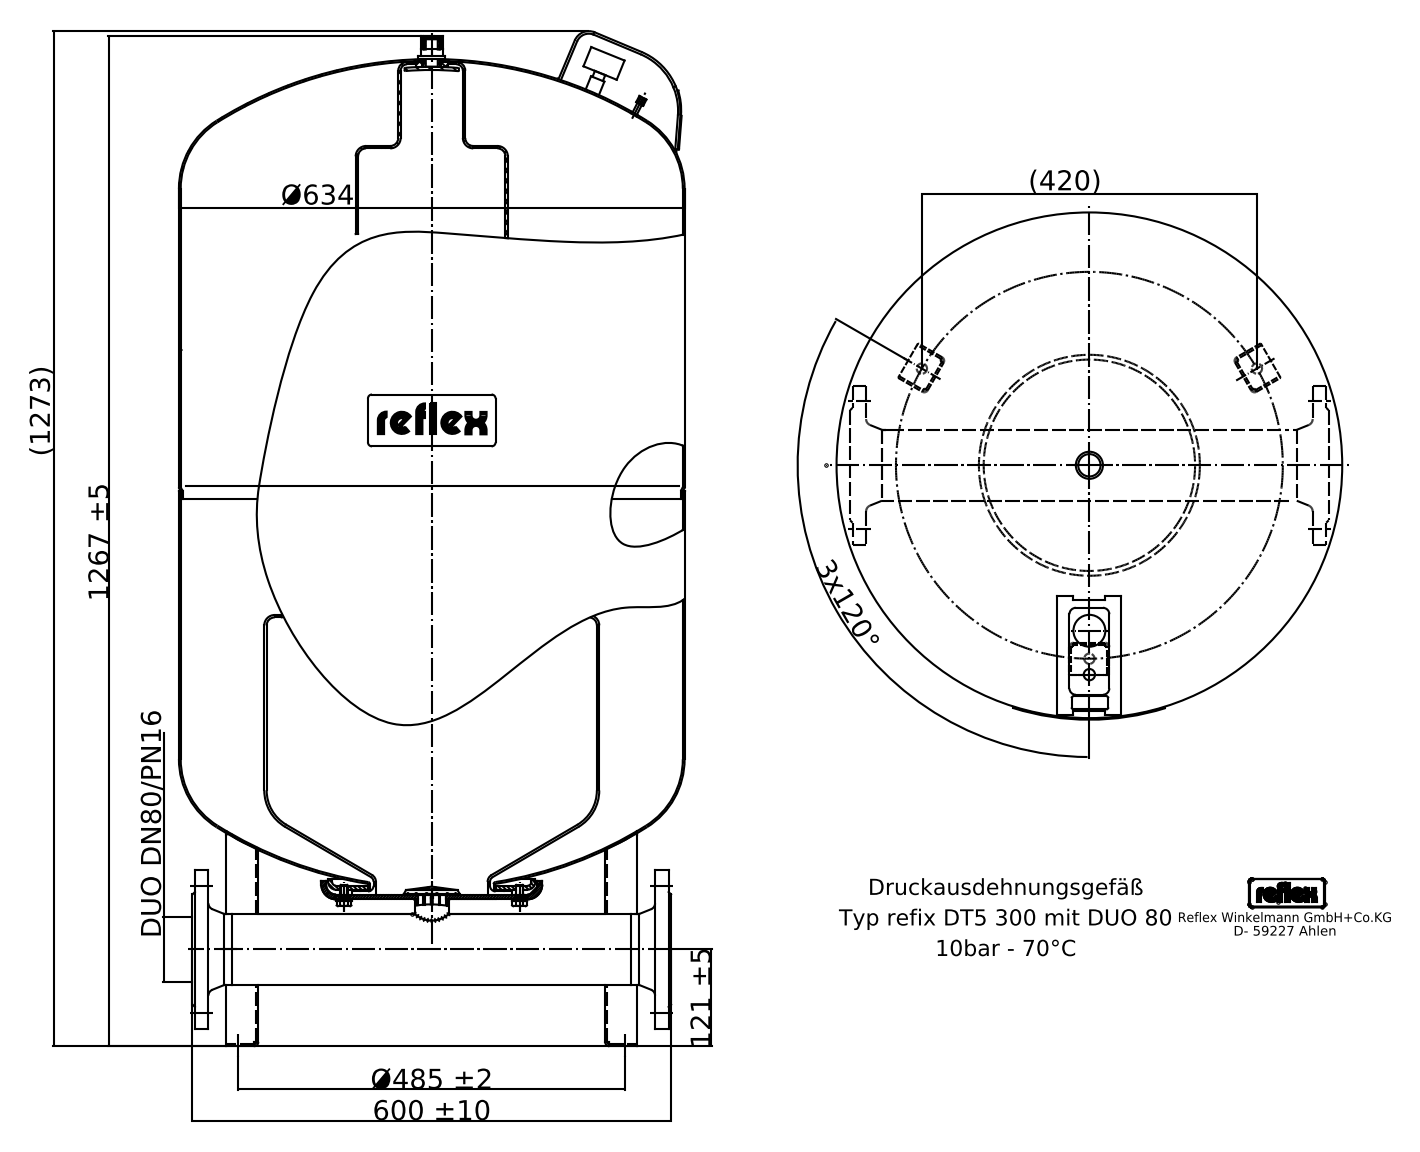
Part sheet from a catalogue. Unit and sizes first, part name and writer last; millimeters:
Units: millimetres
Overall size (bounding box): 1268.4 × 634 × 634
Round holes (diameter × count): ⌀19 ×8, ⌀13.4 ×3, ⌀2.48 ×1, ⌀3.8 ×1, ⌀4.3 ×1, ⌀4.4 ×1, ⌀5.45 ×1, ⌀7 ×1, ⌀8 ×1, ⌀11.4 ×1, ⌀88.9 ×1, ⌀157 ×1
Round bosses / shafts (diameter × count): ⌀10 ×9, ⌀634 ×1, ⌀260 ×1, ⌀230 ×1, ⌀200 ×1, ⌀62 ×1, ⌀42.4 ×1, ⌀34 ×1
Partial cylindrical surfaces — rounded edges, fillets, slot ends (radius × count): R1 ×15, R2.5 ×15, R5 ×15, R5.62 ×4, R2.25 ×3, R3.84 ×2, R6.75 ×2, R8 ×2
Main face-to-face distances: 716, 2.5, 47.5, 170, 886, 6, 176, 892, 50, 45
Hole centre spacings: 80, 113.13, 61.22, 61.24, 147.81, 147.82, 160, 242.5
Volume: 298 700 000 mm³ · Surface area: 4 396 000 mm²
Bodies: 23 solids, 537 faces (223 planar, 193 cylindrical, 121 other)
STEP written by: Mechanical Desktop 2008 (CONFIG_CONTROL_DESIGN)
